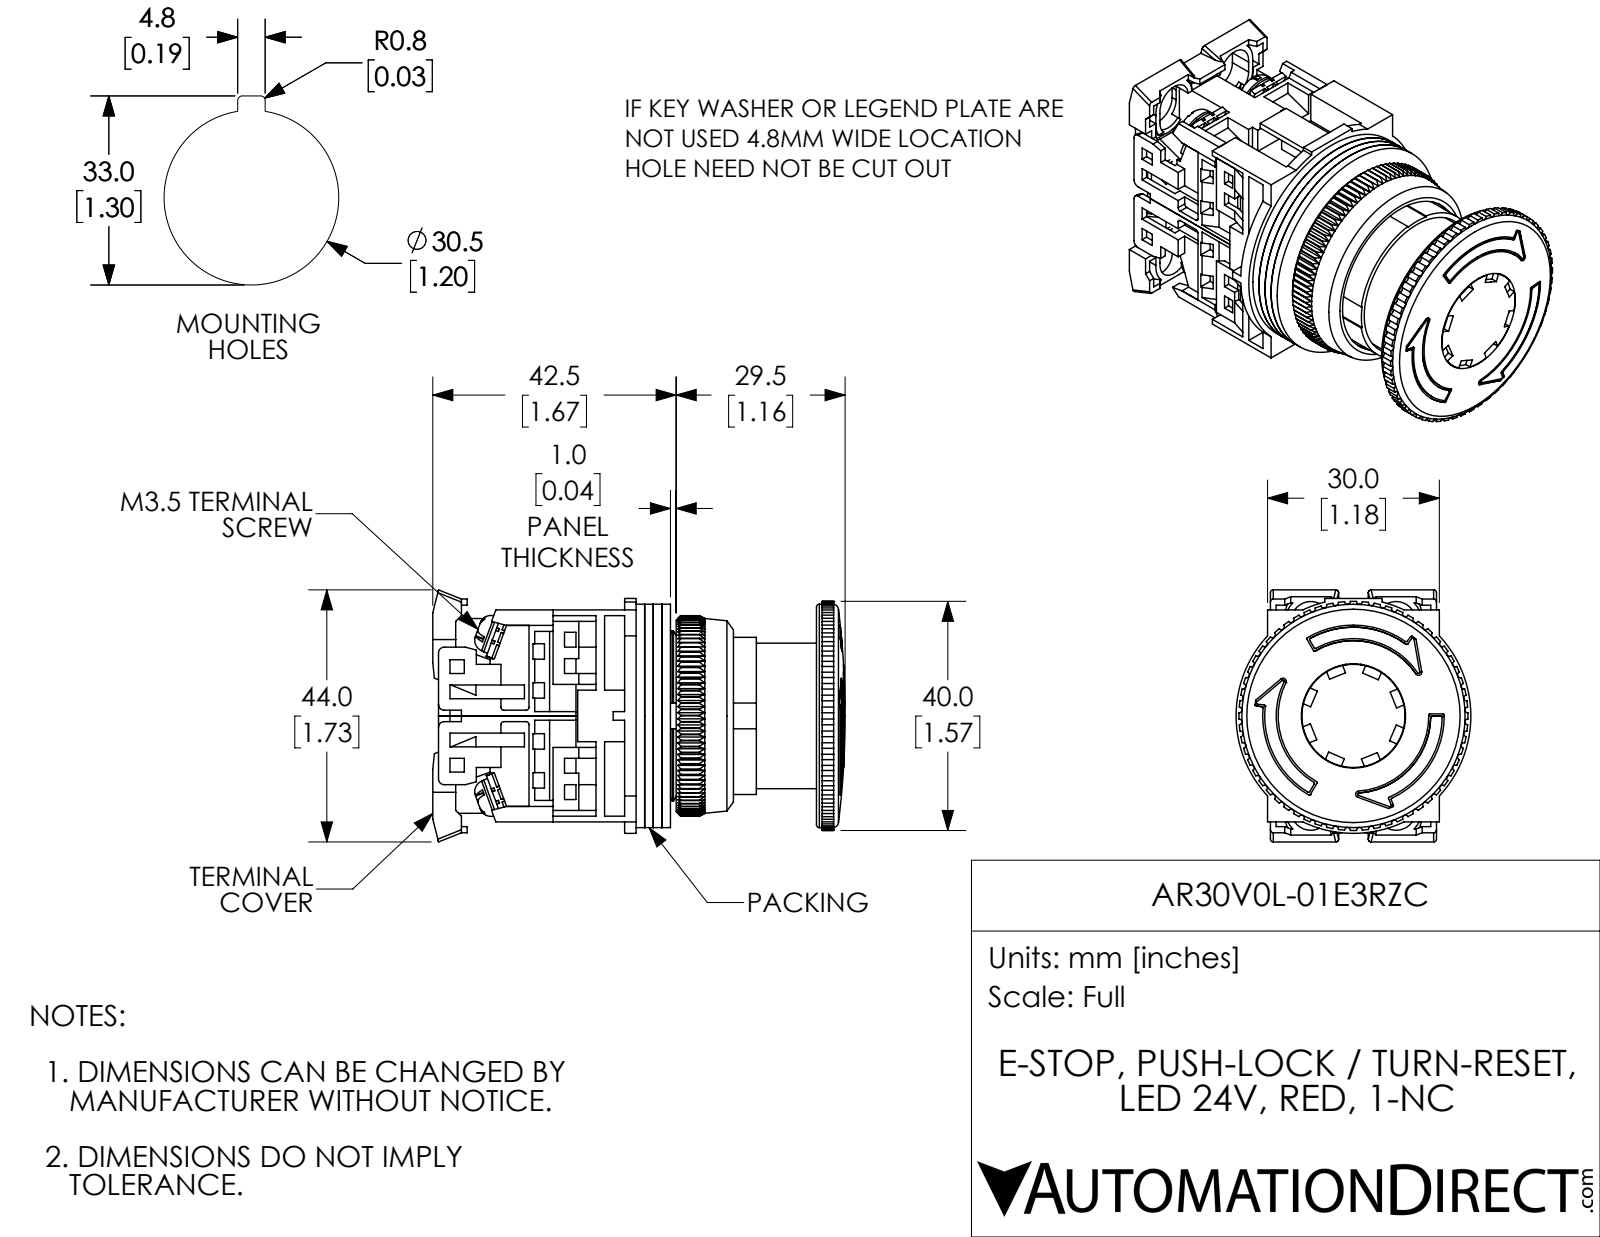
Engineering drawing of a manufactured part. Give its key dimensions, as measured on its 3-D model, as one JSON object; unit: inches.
{"part_name": "AR30V0L-01E3RZC", "step_written_by": "SolidWorks 2017 (AUTOMOTIVE_DESIGN)", "units": "inches", "bodies": {"solids": 25, "faces": 2072, "planar": 1322, "cylindrical": 523, "other": 227}, "overall_size": [2.835, 1.732, 1.614], "volume_in3": 2.694, "surface_area_in2": 71.77, "round_holes": [[0.138, 4], [0.142, 4], [0.118, 1], [0.543, 1], [0.63, 1], [0.709, 1], [0.717, 1], [0.803, 1], [0.921, 1], [1.024, 1], [1.122, 1], [1.173, 1]], "round_bosses_or_shafts": [[0.26, 4], [0.138, 4], [1.535, 1], [1.181, 1], [1, 1]], "partial_cylinders_radius": [[0.02, 72], [0.008, 24], [0.059, 16], [0.022, 6], [0.039, 4], [0.138, 4], [0.177, 4], [0.118, 2]], "face_to_face_distances": [0.059, 0.118, 0.039, 0.177, 1.358, 0.689, 0.079, 1.417, 0.197, 0.138], "hole_center_spacings": [0.579, 0.61]}
